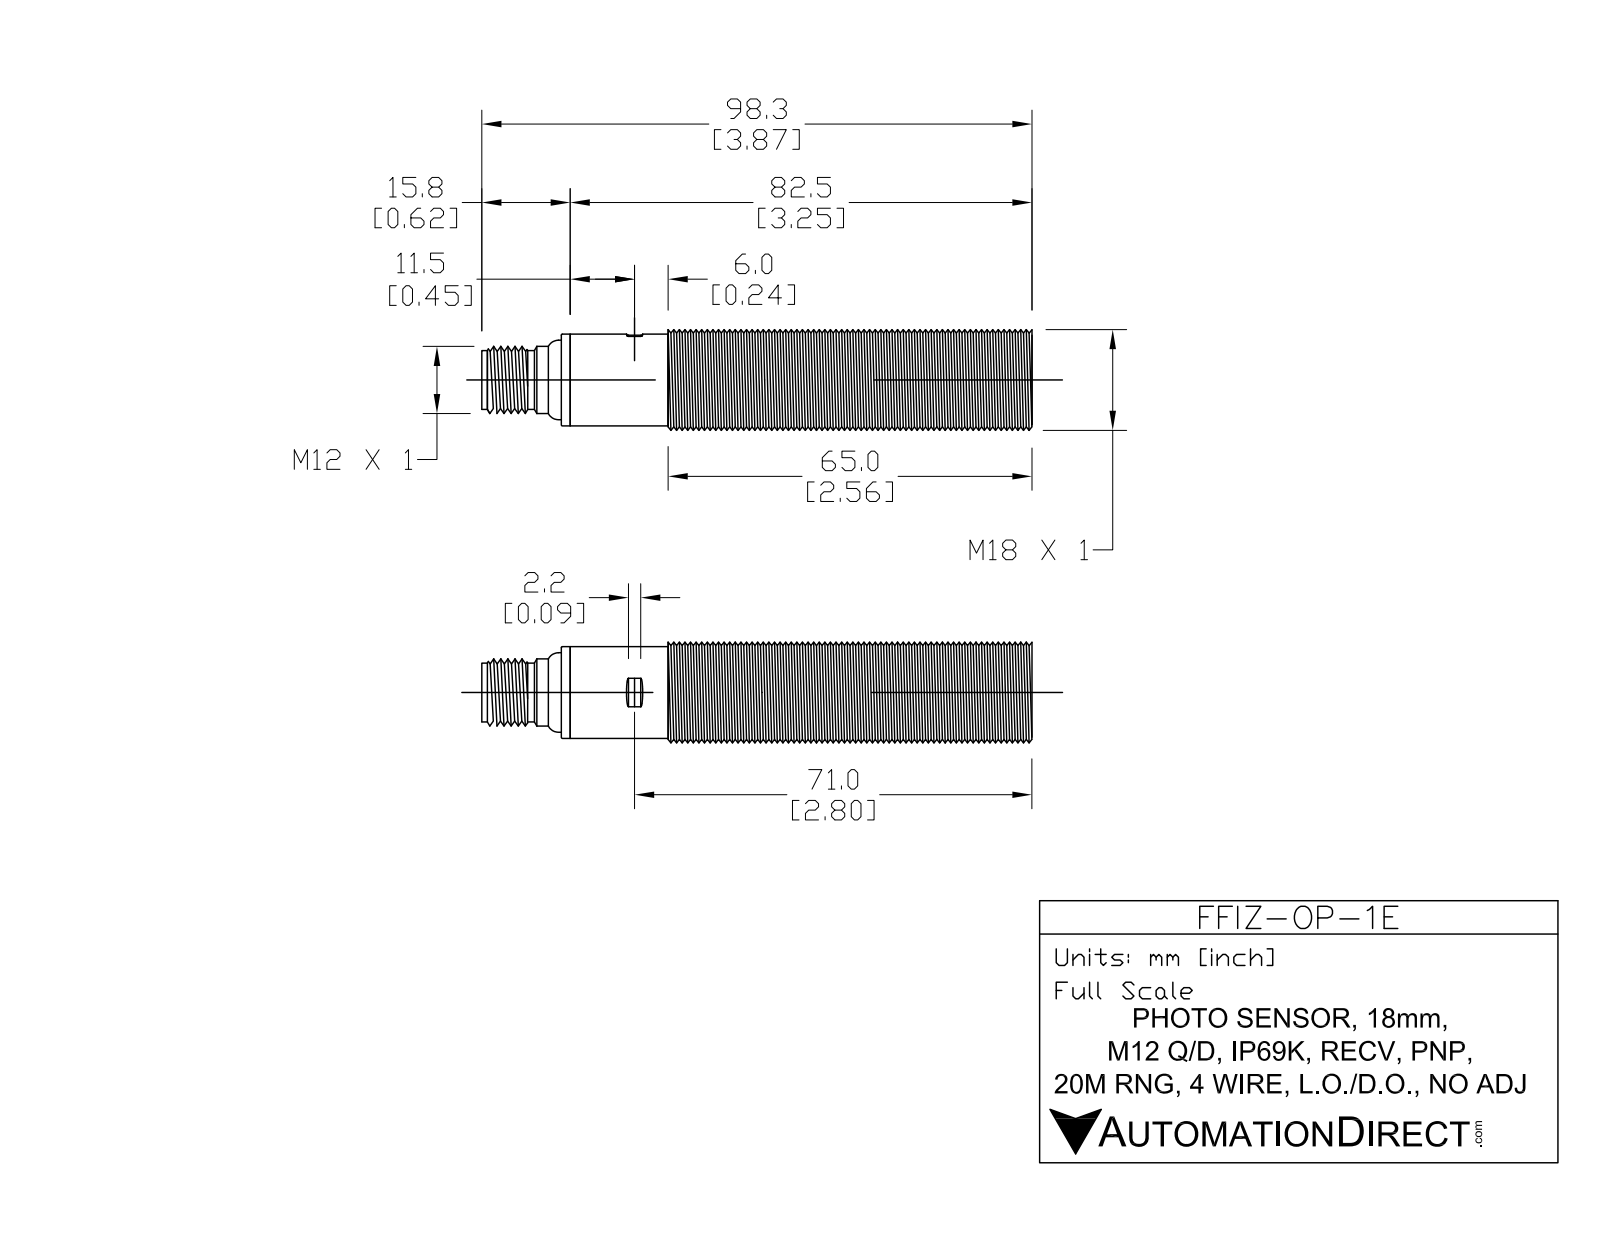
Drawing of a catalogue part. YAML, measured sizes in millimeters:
part_name: "FFIZ-0P-1E"
step_written_by: "SolidWorks 2017 (AUTOMOTIVE_DESIGN)"
units: millimeters
bodies: {solids: 5, faces: 118, planar: 21, cylindrical: 48, other: 49}
overall_size: [83, 18, 18]
volume: 17710
surface_area: 6755
round_holes:
  - {diameter: 7.1, count: 1}
  - {diameter: 8.3, count: 1}
  - {diameter: 12.7, count: 1}
  - {diameter: 14.8, count: 1}
  - {diameter: 15.5, count: 1}
round_bosses_or_shafts:
  - {diameter: 1, count: 4}
  - {diameter: 18, count: 1}
  - {diameter: 16.4, count: 1}
  - {diameter: 15.5, count: 1}
  - {diameter: 15.3, count: 1}
  - {diameter: 14.2, count: 1}
  - {diameter: 12.5, count: 1}
  - {diameter: 12, count: 1}
partial_cylinders:
  - {radius: 0.6, count: 1}
  - {radius: 16, count: 1}
face_to_face_distances: [64.5, 3, 67.5, 0.6, 2.4, 66.9, 69, 68.4, 66, 1.5]
